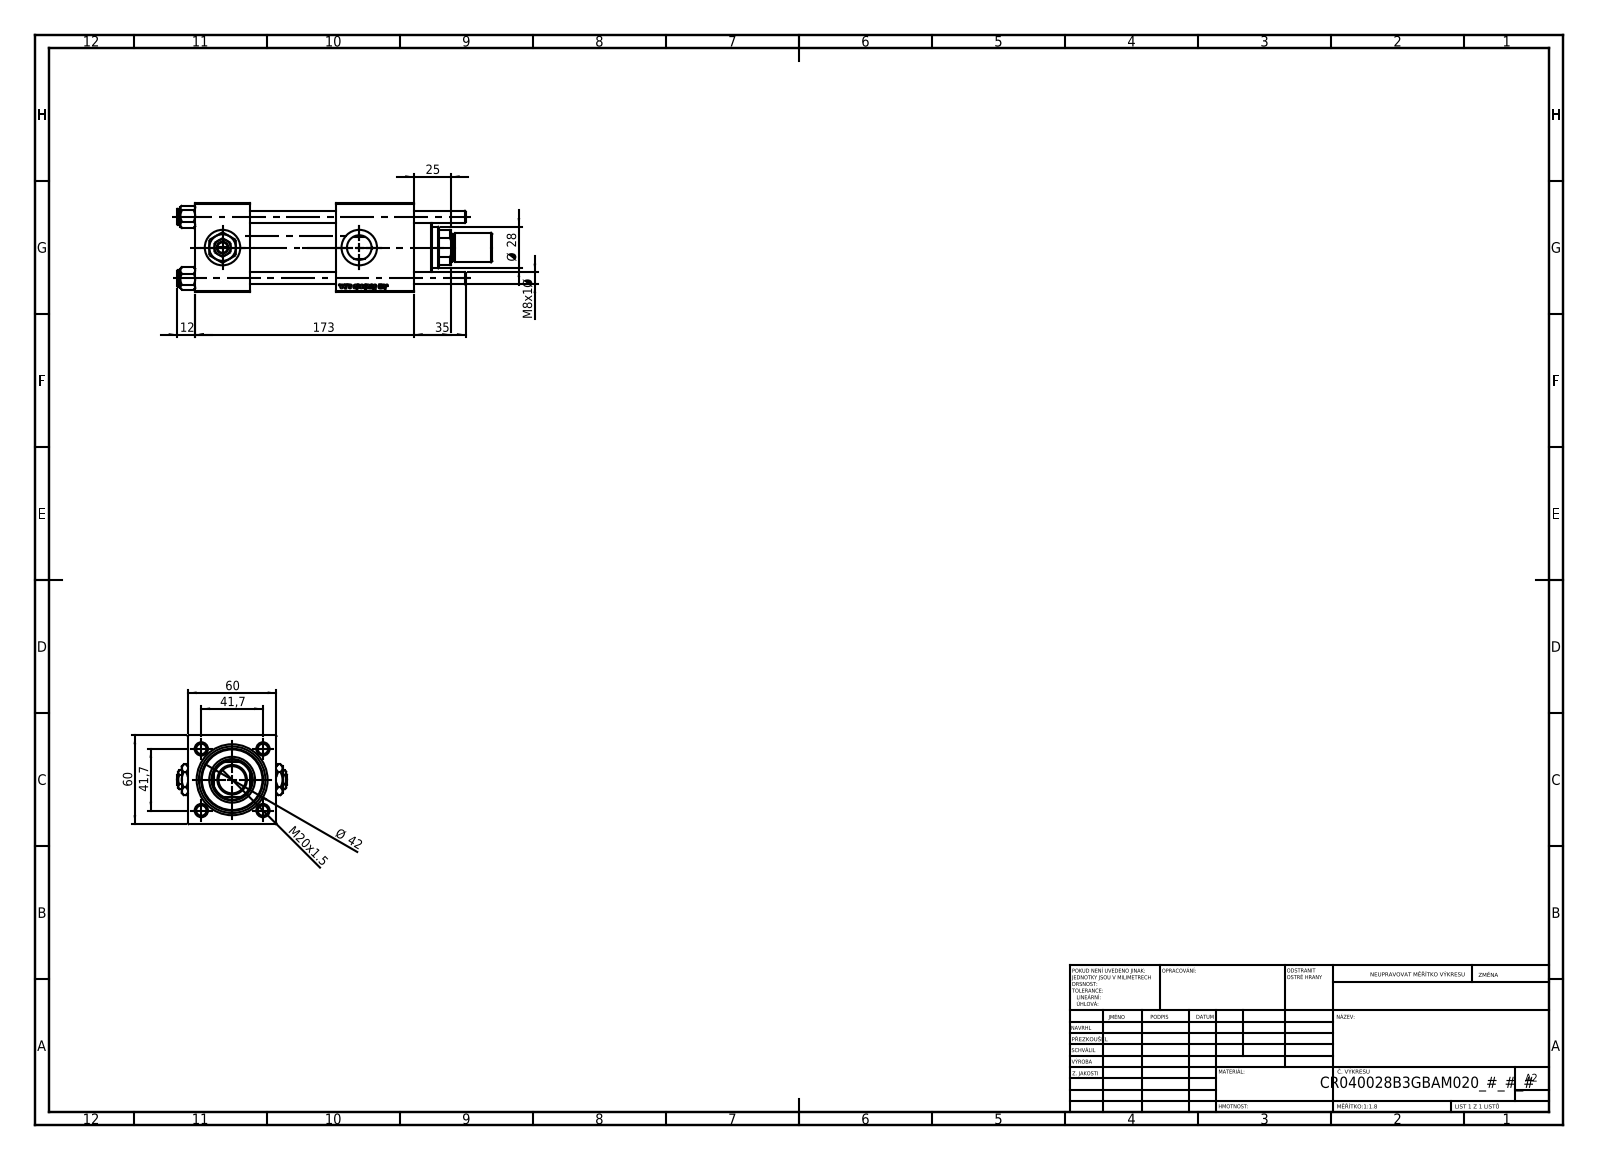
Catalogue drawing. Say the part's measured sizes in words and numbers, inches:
The part is named "Zatka_pro_OIL_PORT; ROD_END_AH; V215CR_VCP_B; NUT_M5_B (+3 more)". Its 3-D file was written by "SolidWorks 2019 (CONFIG_CONTROL_DESIGN)". It is 14 solids with 1273 faces: 485 planar, 92 cylindrical and 696 other. Overall it measures 8.386 by 2.913 by 2.362 inches. Its volume is 26.91 cubic inches and its surface area 194.1 square inches. Round holes: 4 of diameter 0.315, 2 of diameter 0.276, 2 of diameter 0.656, 2 of diameter 0.945, 1 of diameter 0.728, 1 of diameter 1.102, 1 of diameter 1.22, 1 of diameter 1.575, 1 of diameter 1.772. Round bosses or shafts: 4 of diameter 0.433, 1 of diameter 1.811, 1 of diameter 1.654, 1 of diameter 0.787, 1 of diameter 0.709. Partial cylindrical surfaces (rounded edges, fillets, slot ends): 1 of radius 0.531. The main face-to-face distances are 2.362, 1.457, 2.283, 3.74, 2.087, 4.697, 3.24, 0.957, 5.827, 4.37. The hole center spacings are 1.161, 1.642, 2.322, 3.642.
